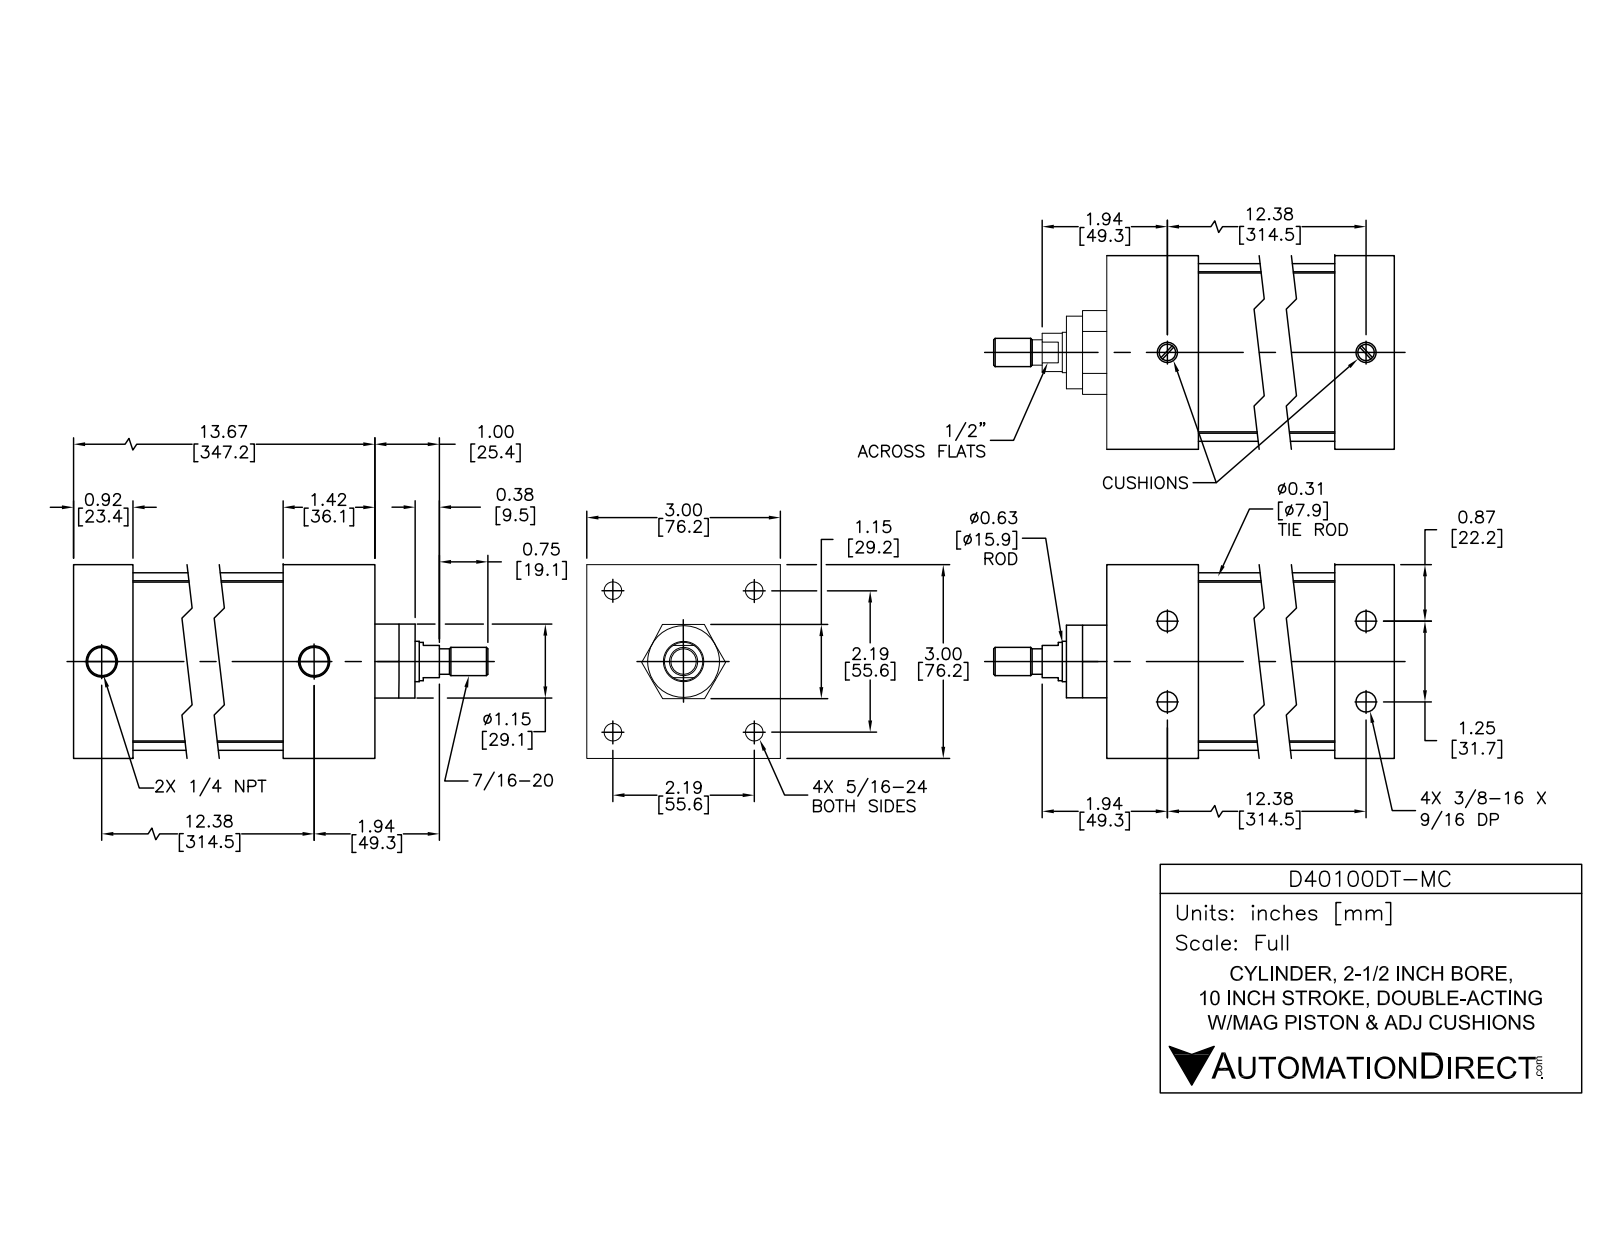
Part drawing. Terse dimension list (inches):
name: D40100DT-MC; D40100DT-M PISTON; D40100DT-M BODY
written by: SolidWorks 2015 (AUTOMOTIVE_DESIGN)
unit: in
bodies: 12 solids, 298 faces (94 planar, 114 cylindrical, 90 other)
size: 15.496 × 3 × 3
volume: 45.06 in³; area: 372.6 in²
holes: 4× ⌀0.267, 4× ⌀0.307, 4× ⌀0.359, 4× ⌀0.5, 2× ⌀0.297, 2× ⌀0.477, 1× ⌀0.625, 1× ⌀0.628, 1× ⌀2.5
bosses: 4× ⌀0.484, 4× ⌀0.313, 4× ⌀0.282, 1× ⌀2.75, 1× ⌀2.497, 1× ⌀1.12, 1× ⌀0.622, 1× ⌀0.59
rounds: 4× R0.3
face distances: 3, 0.08, 11.326, 13.746, 12.726, 1.02, 1.42, 11.306, 12.326, 1
hole spacings: 1.556, 2.2, 12.386, 12.37, 0.625, 0.625, 1.25, 3.111
